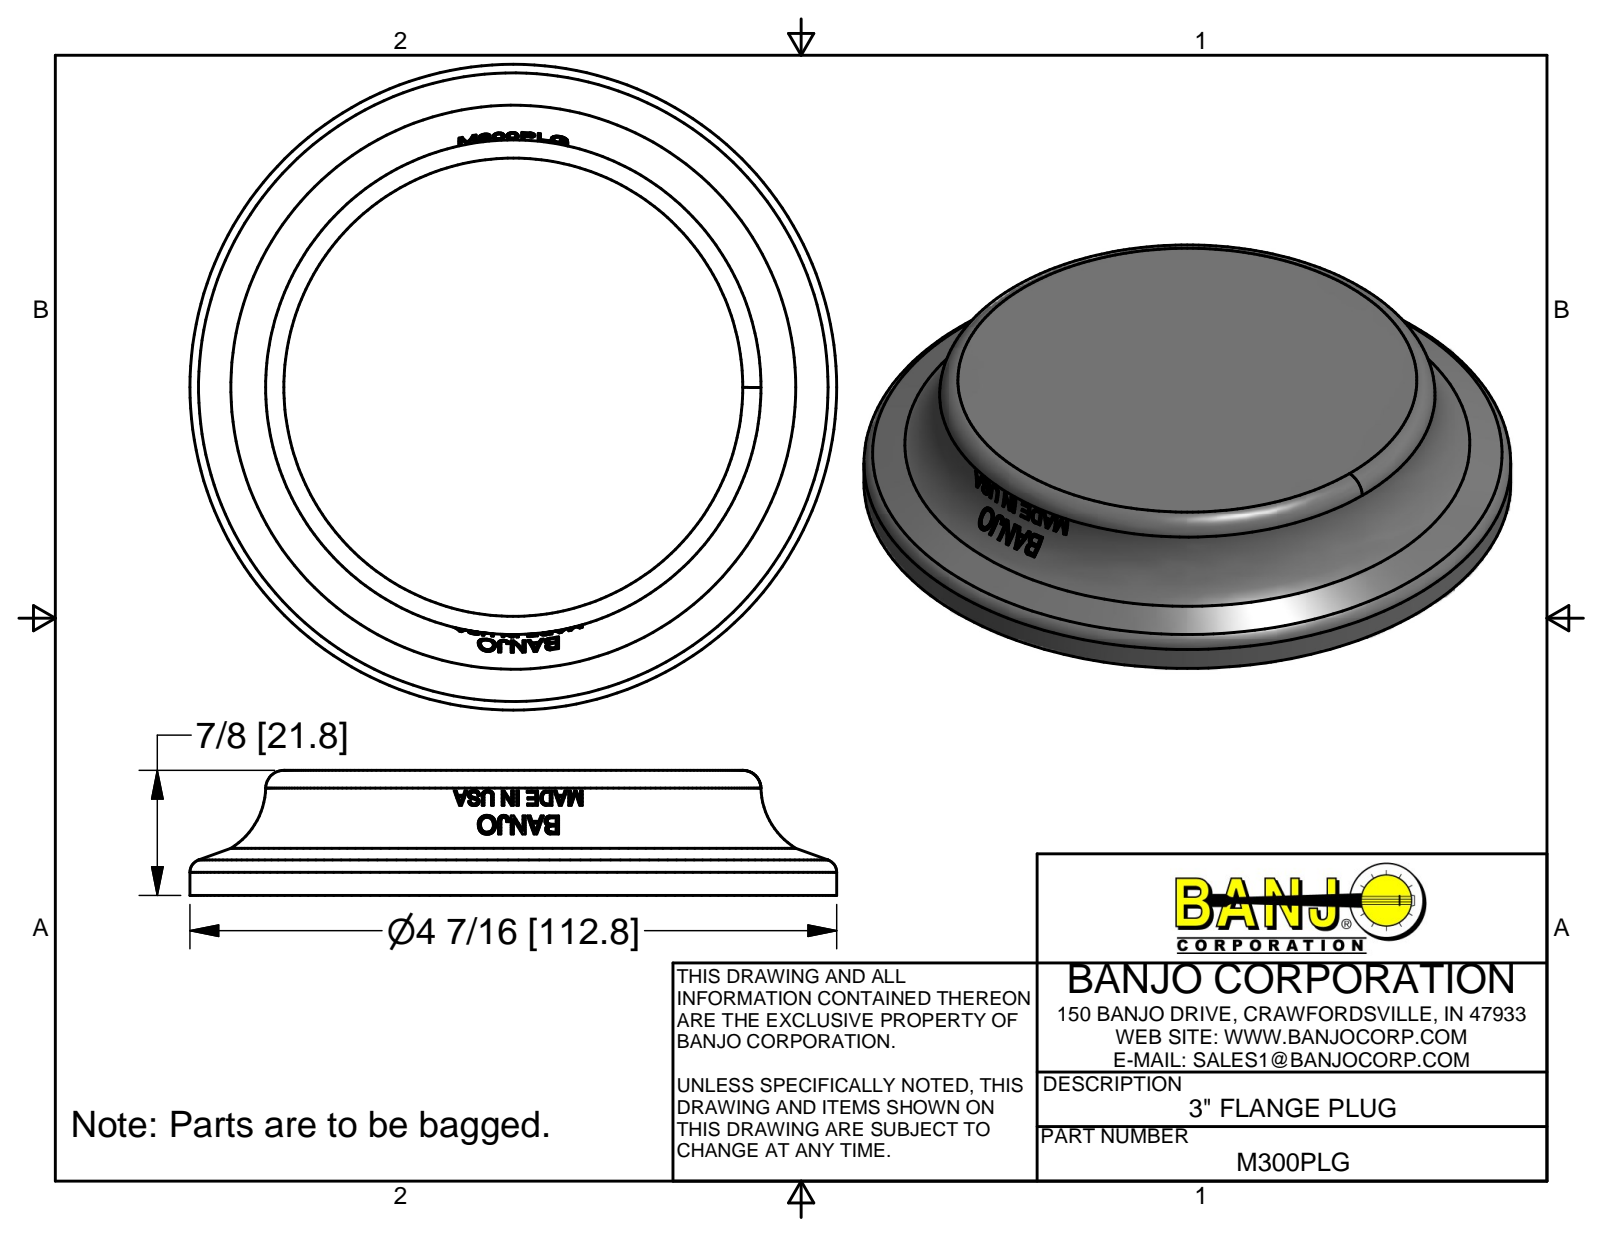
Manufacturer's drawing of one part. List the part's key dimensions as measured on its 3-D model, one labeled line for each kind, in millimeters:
Part name (STEP PRODUCT): M300PLG; TITLBLKB; IQSTAG
STEP written by: Mechanical Desktop 2009 (CONFIG_CONTROL_DESIGN)
Units: millimetres
Bodies: 1 solid, 23 faces (5 planar, 8 cylindrical, 10 other)
Overall size (bounding box): 4.44 × 4.44 × 0.86
Volume: 6 mm³ · Surface area: 43 mm²
Round holes (diameter × count): ⌀3 ×1, ⌀3.75 ×1
Round bosses / shafts (diameter × count): ⌀4.44 ×1, ⌀3.4 ×1
Main face-to-face distances: 0.41, 0.45, 0.86, 0.35, 0.76, 0.33, 0.53
